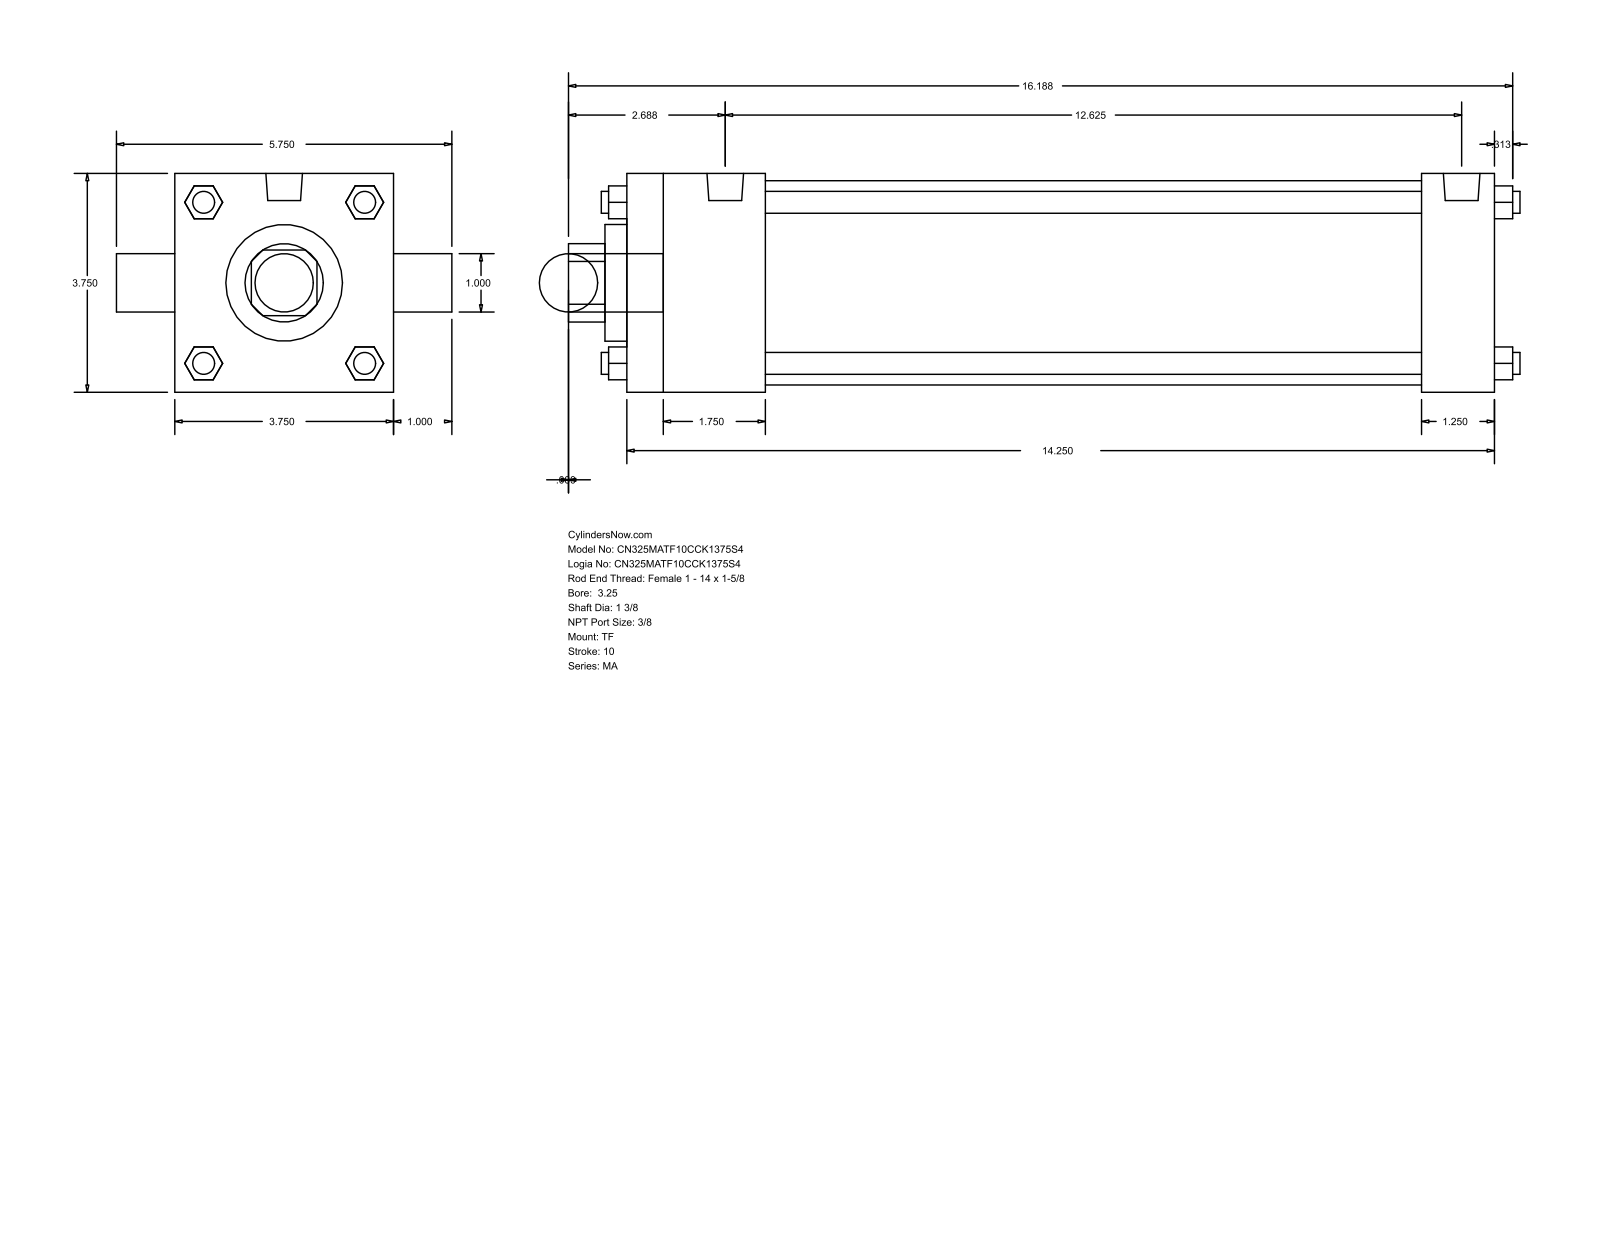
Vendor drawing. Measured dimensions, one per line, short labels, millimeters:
name: MA_TF__0325_1.375
written by: GSSL Pune (CONFIG_CONTROL_DESIGN)
unit: mm
bodies: 0 solids, 120 faces (92 planar, 28 cylindrical, 0 other)
size: 414.34 × 146.05 × 95.25
holes: 1× ⌀25.4, 1× ⌀34.92, 1× ⌀50.8, 1× ⌀88.9
bosses: 4× ⌀9.53, 3× ⌀11.11, 2× ⌀15.93, 1× ⌀25.4
rounds: 1× R17.06
face distances: 95.24, 377.83, 60.32, 346.08, 285.76, 317.51, 31.75, 9.52, 69.84, 355.6
